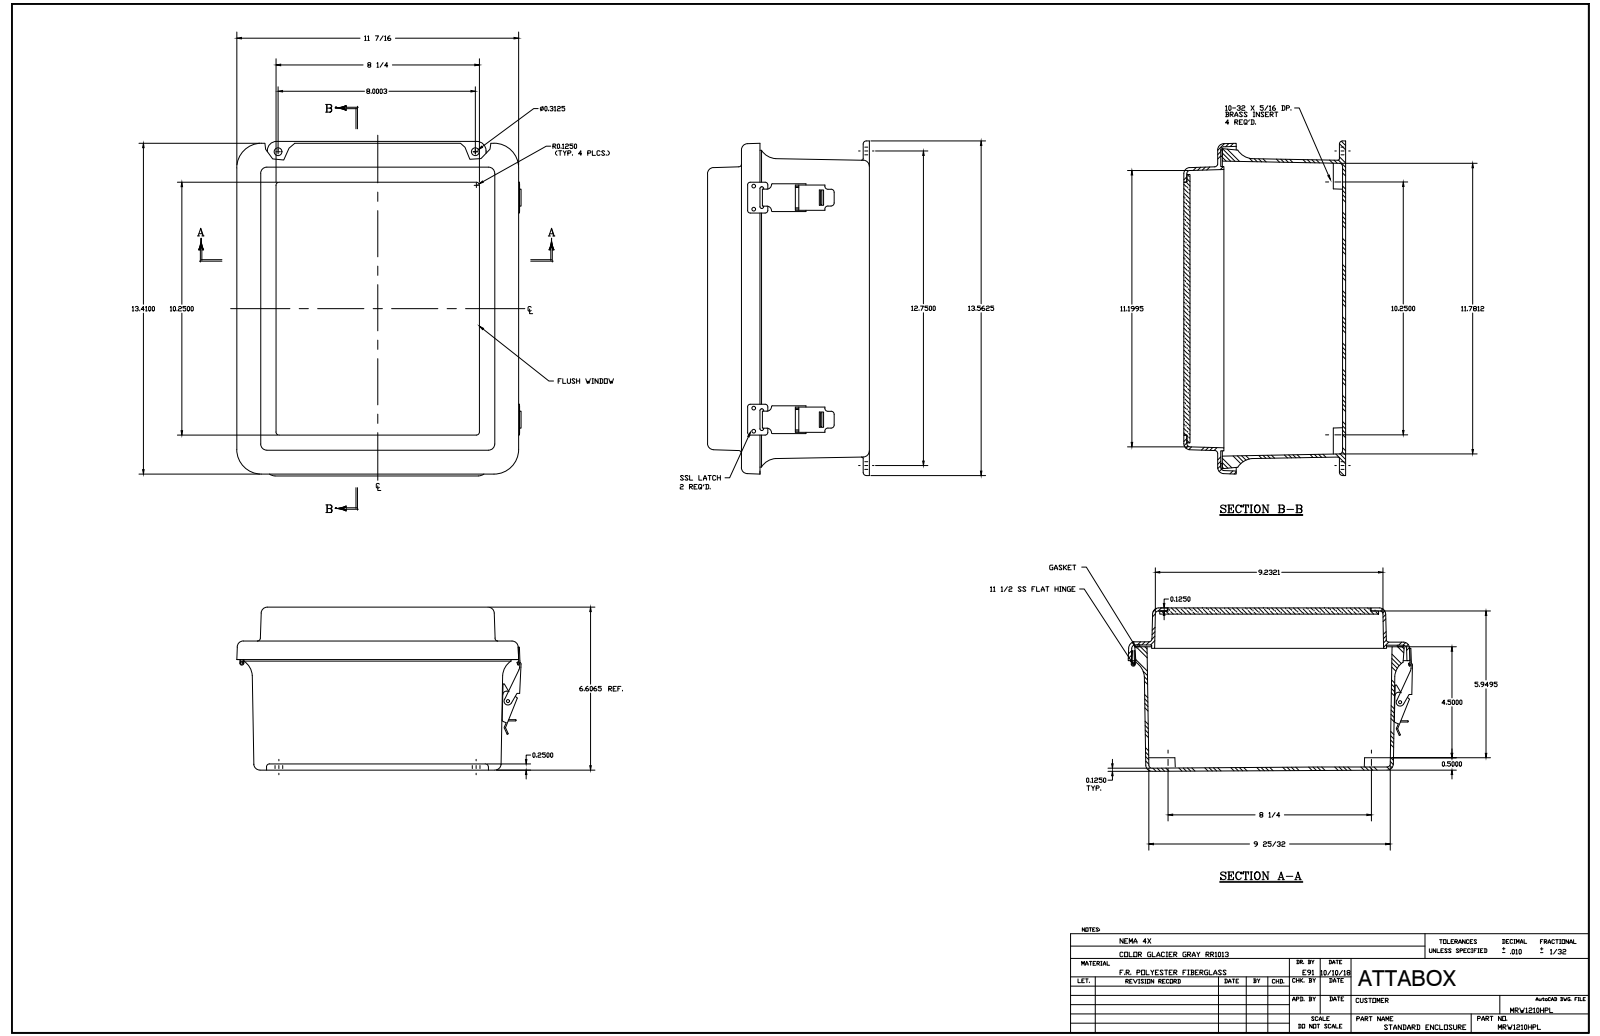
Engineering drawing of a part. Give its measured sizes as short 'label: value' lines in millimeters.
name: MRW1210HPL
written by: SolidWorks 2018 (AUTOMOTIVE_DESIGN)
unit: mm
bodies: 39 solids, 1073 faces (461 planar, 441 cylindrical, 171 other)
size: 344.5 × 293 × 167.3
volume: 1 709 000 mm³; area: 869 000 mm²
holes: 20× ⌀3.6, 8× ⌀2.6, 8× ⌀3.3, 5× ⌀3.9, 4× ⌀3.3, 4× ⌀4, 4× ⌀5.5, 2× ⌀3.4, 2× ⌀9.5, 1× ⌀2.2, 1× ⌀2.2, 1× ⌀3.4
bosses: 12× ⌀3.2, 8× ⌀6.4, 4× ⌀6.9, 4× ⌀3.2, 1× ⌀7.6, 1× ⌀4.3, 1× ⌀3.9, 1× ⌀3.9
rounds: 32× R3.2, 20× R0.4, 20× R0.8, 20× R6.4, 16× R1.1, 12× R0.8, 9× R0.6, 6× R1.5
face distances: 3.2, 164.2, 6.4, 161, 157.8, 167.3, 128.9, 35.2, 125.7, 32.1
hole spacings: 228.6, 229.4, 23.8, 19.1, 92.1, 6.4, 19.1, 34.2
